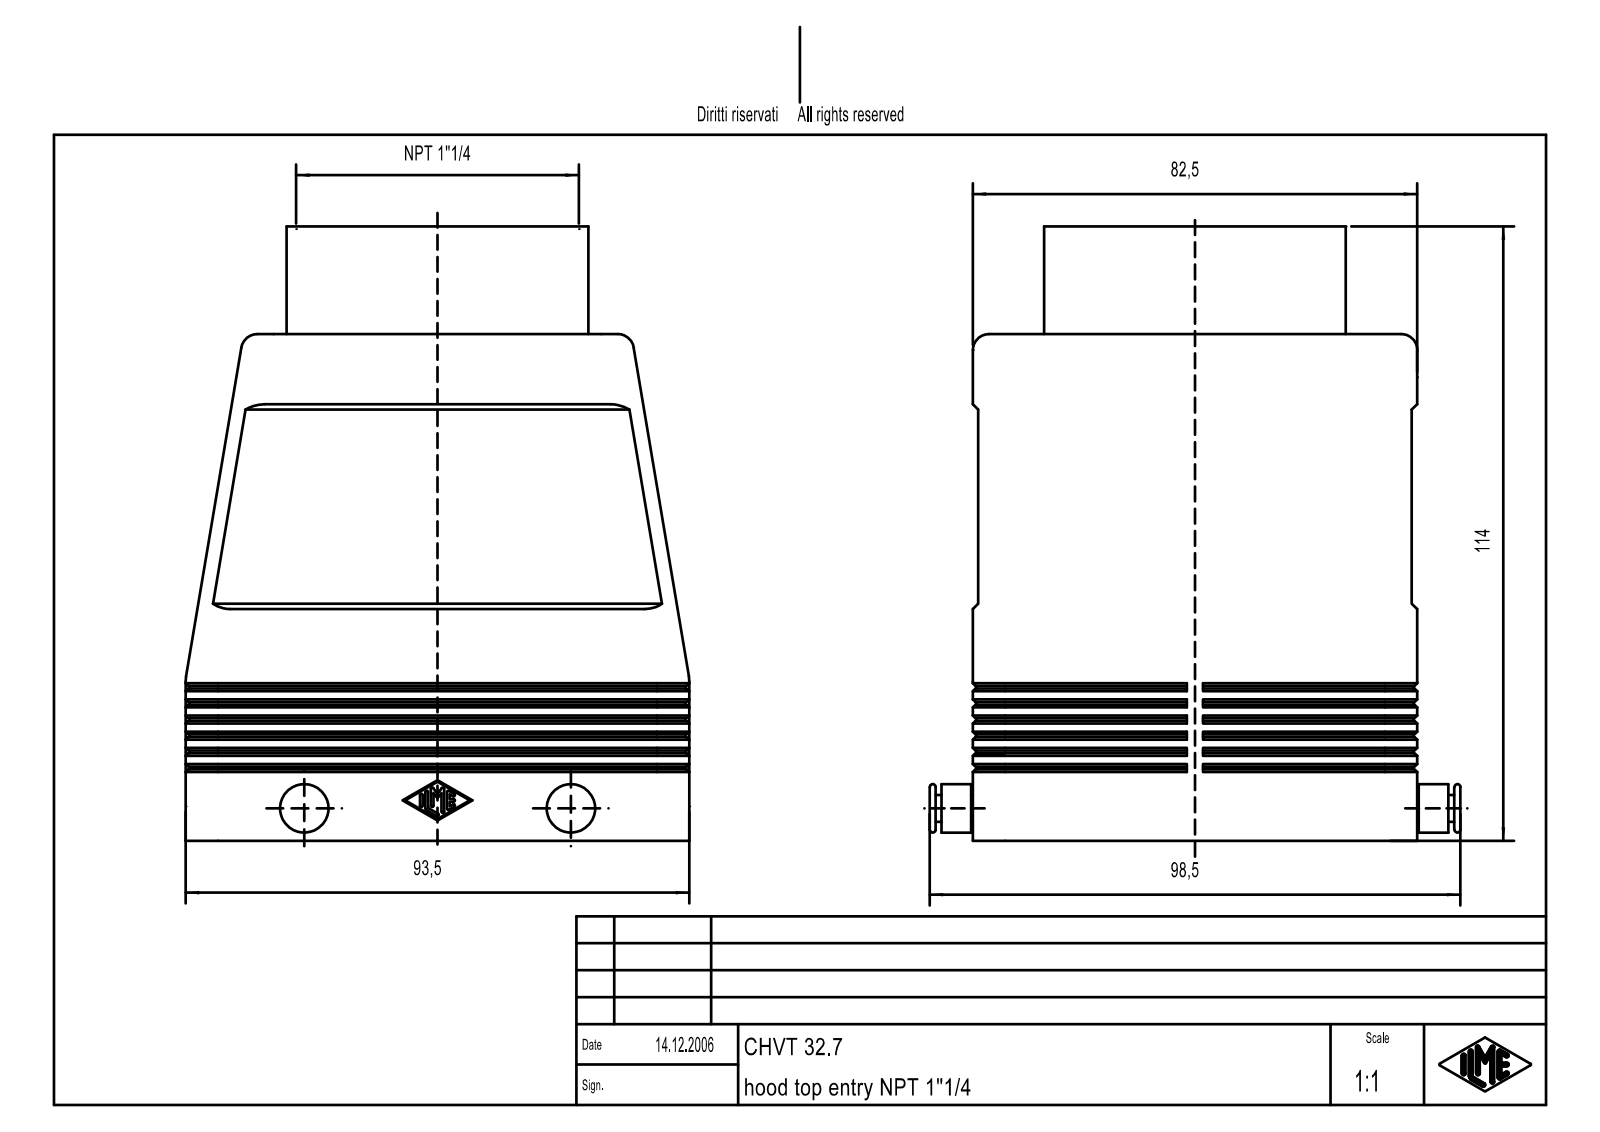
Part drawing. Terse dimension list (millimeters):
name: CHV_32.42; CHV_32.42.stp
written by: Creo Elements/Direct Modeling 18.0B 02-Dec-2011 (C) Parametric Technology GmbH (AUTOMOTIVE_DESIGN)
unit: mm
bodies: 1 solid, 511 faces (275 planar, 150 cylindrical, 86 other)
size: 114 × 98.5 × 93.5
volume: 178 135 mm³; area: 81 194 mm²
holes: 8× ⌀2.46, 8× ⌀3.5
bosses: 2× ⌀9, 2× ⌀5, 1× ⌀65, 1× ⌀56
rounds: 14× R0.25, 12× R2, 10× R6, 4× R3, 4× R5.3
face distances: 4, 78.5, 3, 1, 74.5, 82.5, 81.5, 77.5, 7, 71.5
hole spacings: 27, 35, 77.5, 82.07, 85.04, 8, 62, 77.91
